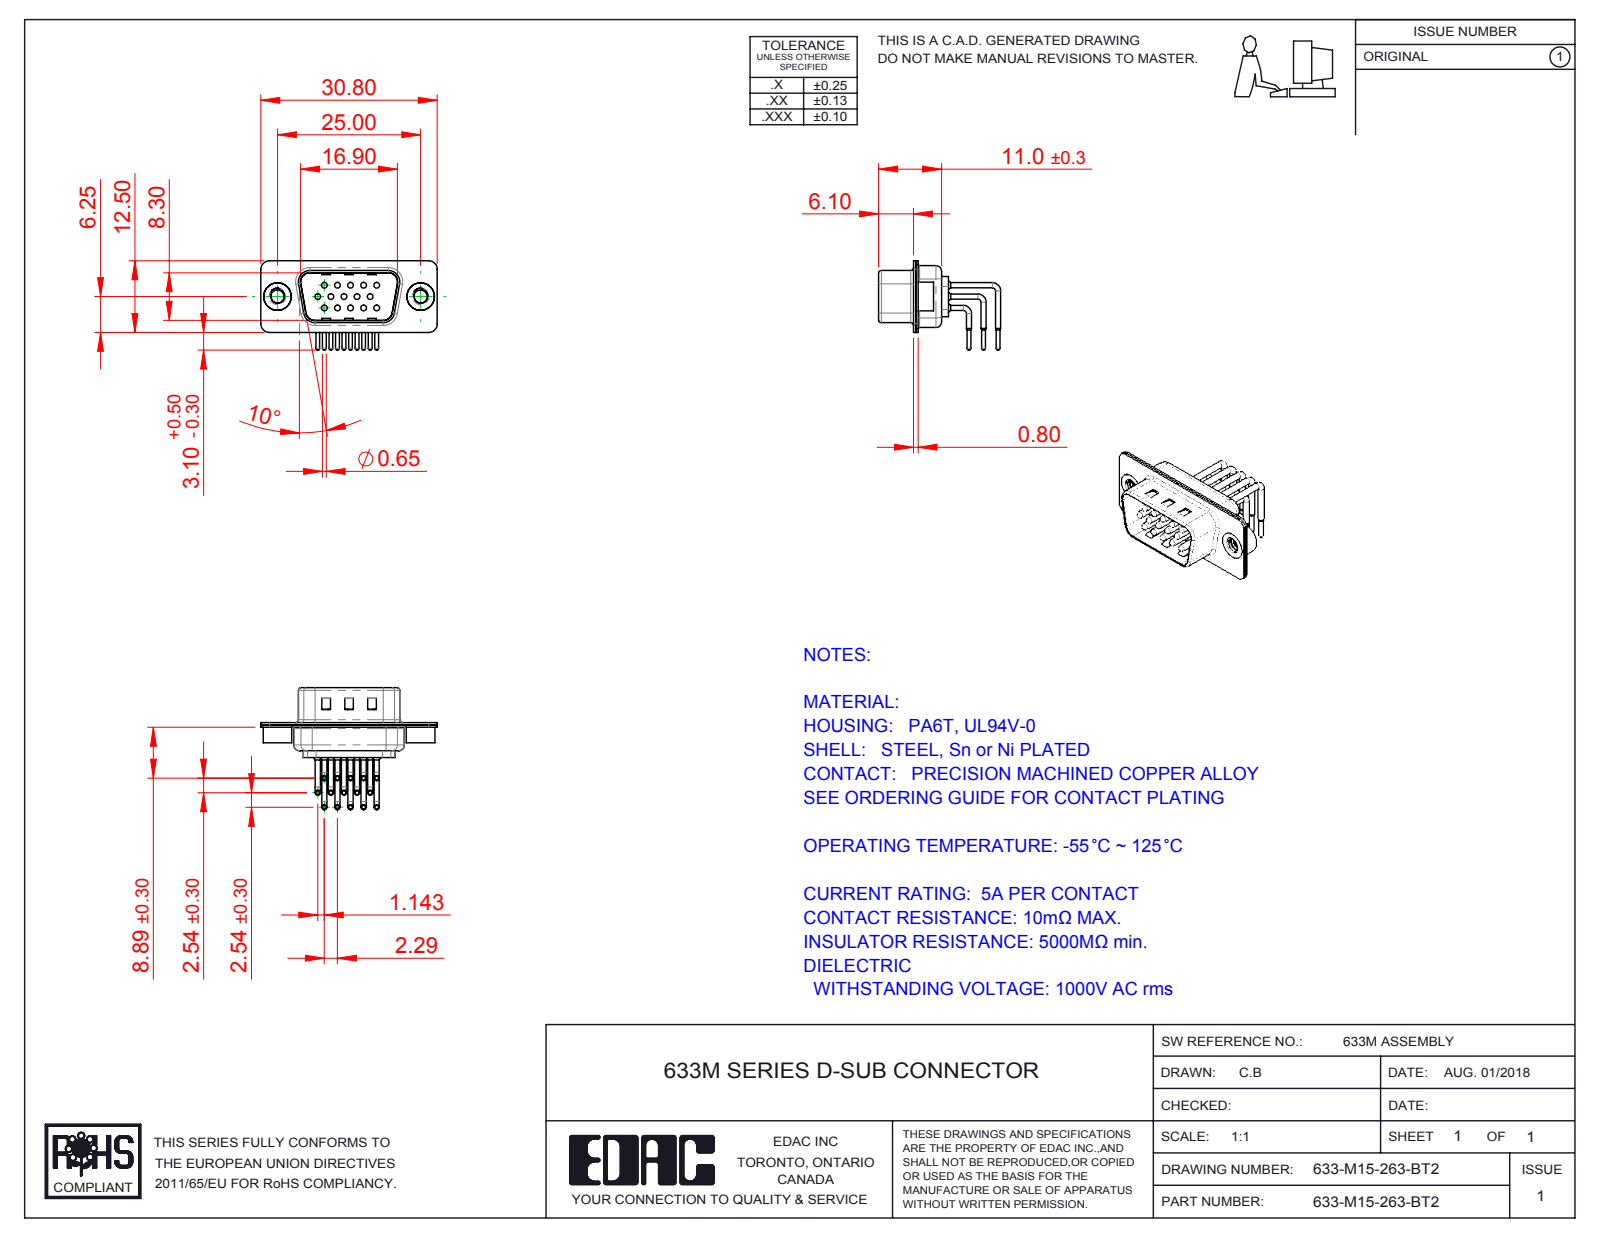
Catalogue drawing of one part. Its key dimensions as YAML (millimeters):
part_name: "633M Contact Row 3; 633M Housing_15 Contacts; 633M Contact Row 2; 633M Contact Row 1 (+4 more)"
step_written_by: "SolidWorks 2016 (CONFIG_CONTROL_DESIGN)"
units: millimeters
bodies: {solids: 20, faces: 1954, planar: 1067, cylindrical: 669, other: 218}
overall_size: [30.8, 21.32, 15.6]
volume: 1451
surface_area: 4630
round_holes:
  - {diameter: 1, count: 15}
  - {diameter: 1.7, count: 15}
  - {diameter: 2, count: 15}
  - {diameter: 2.26, count: 2}
  - {diameter: 4, count: 2}
  - {diameter: 4.8, count: 2}
round_bosses_or_shafts:
  - {diameter: 0.9, count: 30}
  - {diameter: 1.5, count: 15}
  - {diameter: 0.65, count: 15}
  - {diameter: 5, count: 2}
  - {diameter: 4.9, count: 2}
partial_cylinders:
  - {radius: 1.5, count: 16}
  - {radius: 1.01, count: 15}
  - {radius: 2, count: 12}
  - {radius: 0.5, count: 8}
  - {radius: 1.6, count: 8}
  - {radius: 0.25, count: 4}
  - {radius: 0.6, count: 4}
  - {radius: 0.65, count: 4}
face_to_face_distances: [0.4, 0.85, 0.8, 9.55, 1.25, 10.4, 1.5, 8.7, 1.9, 0.35]
hole_center_spacings: [3.96, 2.28, 2.29, 4.57, 6.05, 6.86, 7.92, 6.04]
